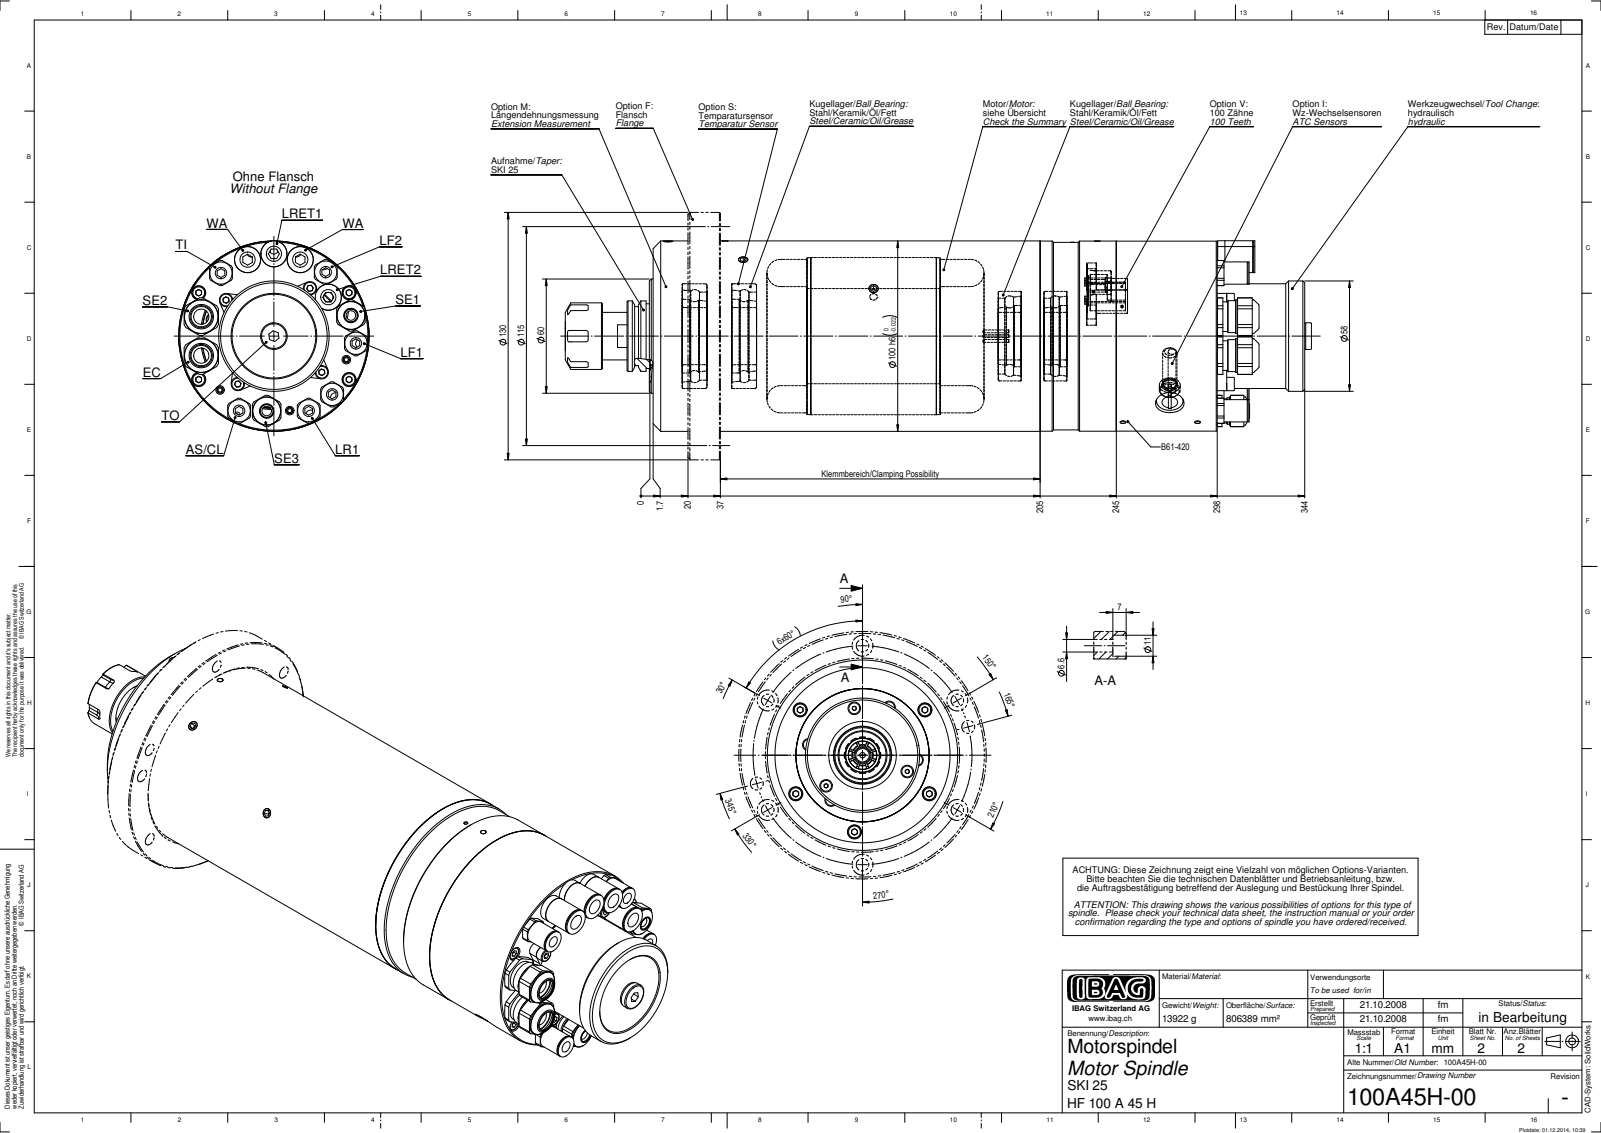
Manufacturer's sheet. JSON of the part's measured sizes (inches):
{"part_name": "100A45H-00", "step_written_by": "SolidWorks 2012 (CONFIG_CONTROL_DESIGN)", "units": "inches", "bodies": {"solids": 0, "faces": 879, "planar": 366, "cylindrical": 317, "other": 196}, "overall_size": [15.431, 3.939, 3.937], "round_holes": [[0.291, 9], [0.236, 8], [0.315, 4], [0.177, 3], [0.591, 3], [0.421, 2], [0.638, 2], [0.197, 1], [0.264, 1], [0.394, 1], [2.756, 1]], "round_bosses_or_shafts": [[0.461, 8], [0.224, 7], [0.276, 4], [0.701, 2], [0.661, 2], [0.614, 2], [0.551, 2], [0.539, 2]], "partial_cylinders_radius": [[0.039, 12], [0.197, 8], [0.26, 8], [0.39, 2], [0.325, 1], [0.571, 1]], "face_to_face_distances": [9.579, 2.087, 11.665, 0.72, 8.858, 10.945, 0.079, 13.457, 0.799, 9.657], "hole_center_spacings": [1.703, 1.795, 1.056, 1.5, 1.575, 1.594, 2.845, 3.13]}
